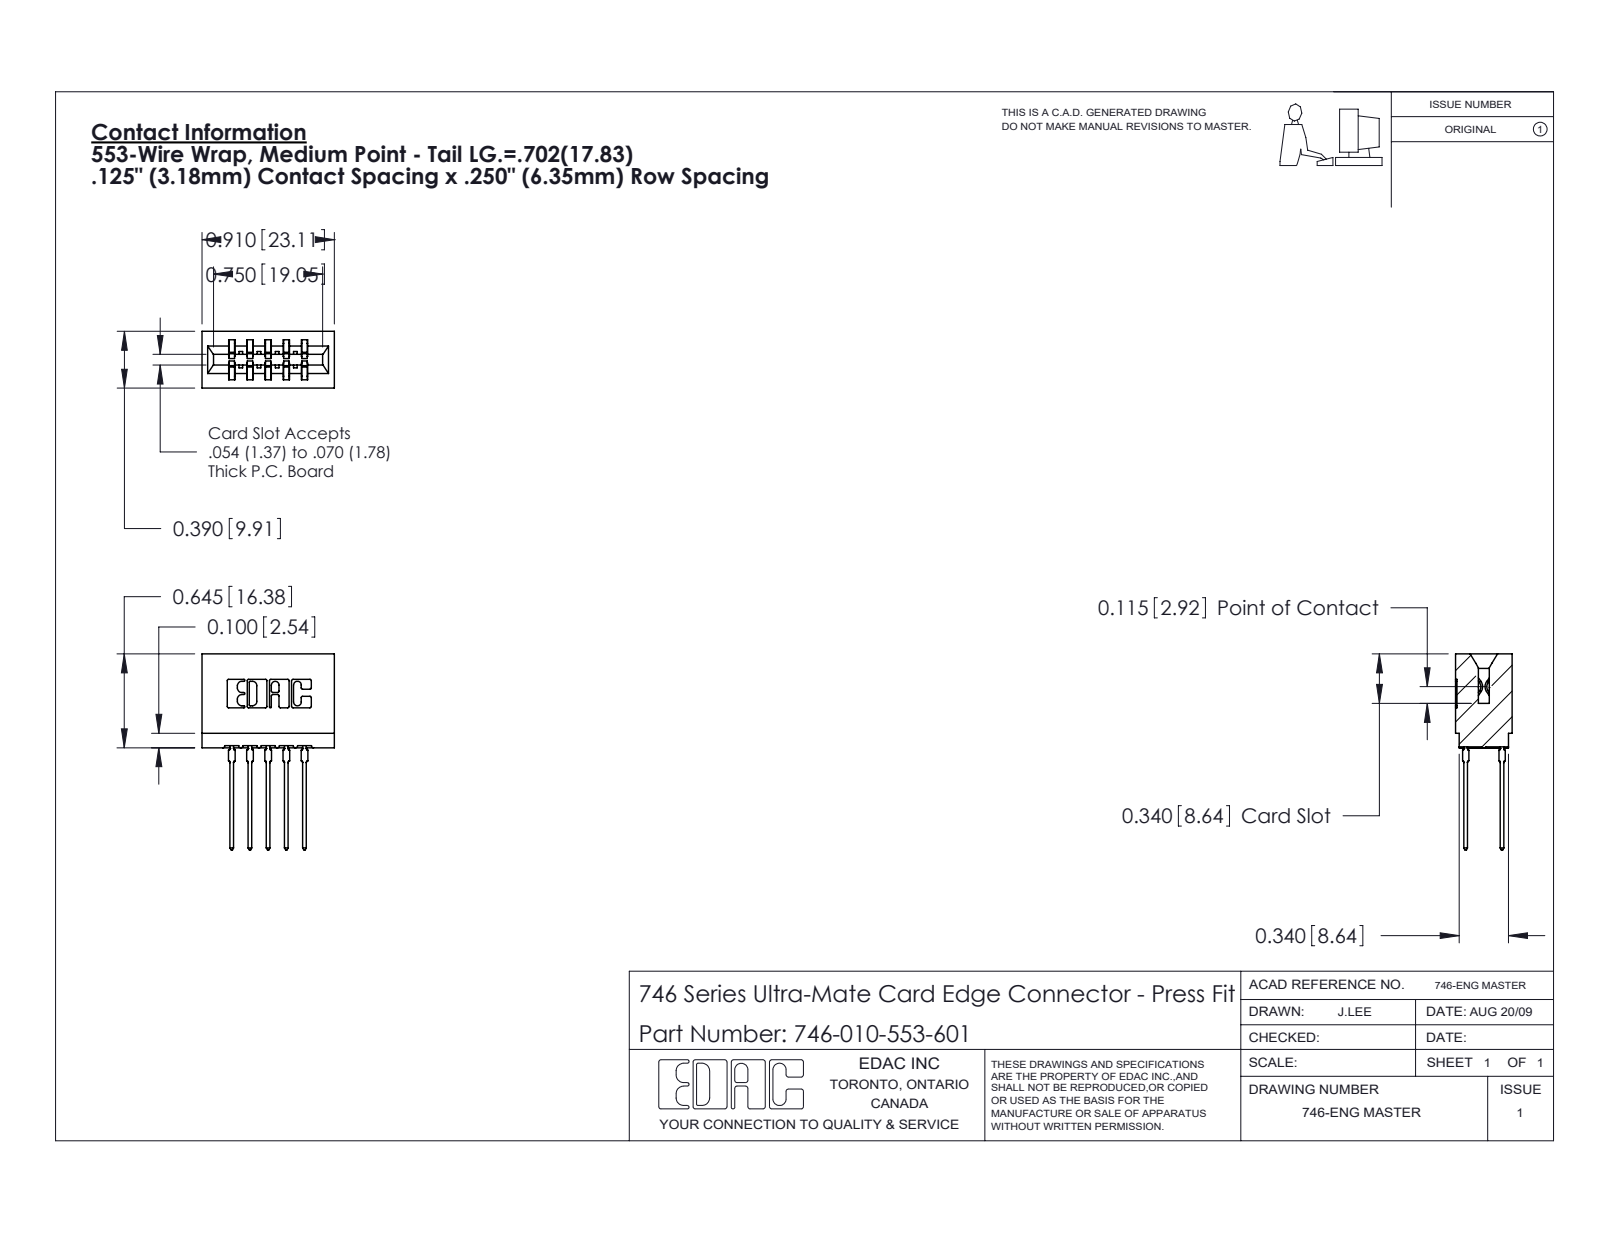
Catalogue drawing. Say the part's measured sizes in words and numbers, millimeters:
The part is named "746-292-001_553; 746-010-553-601; 746 Part_.340 Slot Depth - 01". Its 3-D file was written by "SolidWorks 2020 (CONFIG_CONTROL_DESIGN)". It is 11 solids with 992 faces: 515 planar, 217 cylindrical and 260 other. Overall it measures 34.2 by 23.1 by 9.9 millimeters. Its volume is 2 920 cubic millimeters and its surface area 3 802 square millimeters. Partial cylindrical surfaces (rounded edges, fillets, slot ends): 22 of radius 0.3, 20 of radius 0.5, 8 of radius 0.1, 8 of radius 0.3, 6 of radius 0.2, 6 of radius 0.4, 6 of radius 0.8, 3 of radius 0.7. The main face-to-face distances are 6.4, 1.4, 8.5, 1.1, 3.2, 3.2, 2.1, 0.6, 9.9, 7.8.
